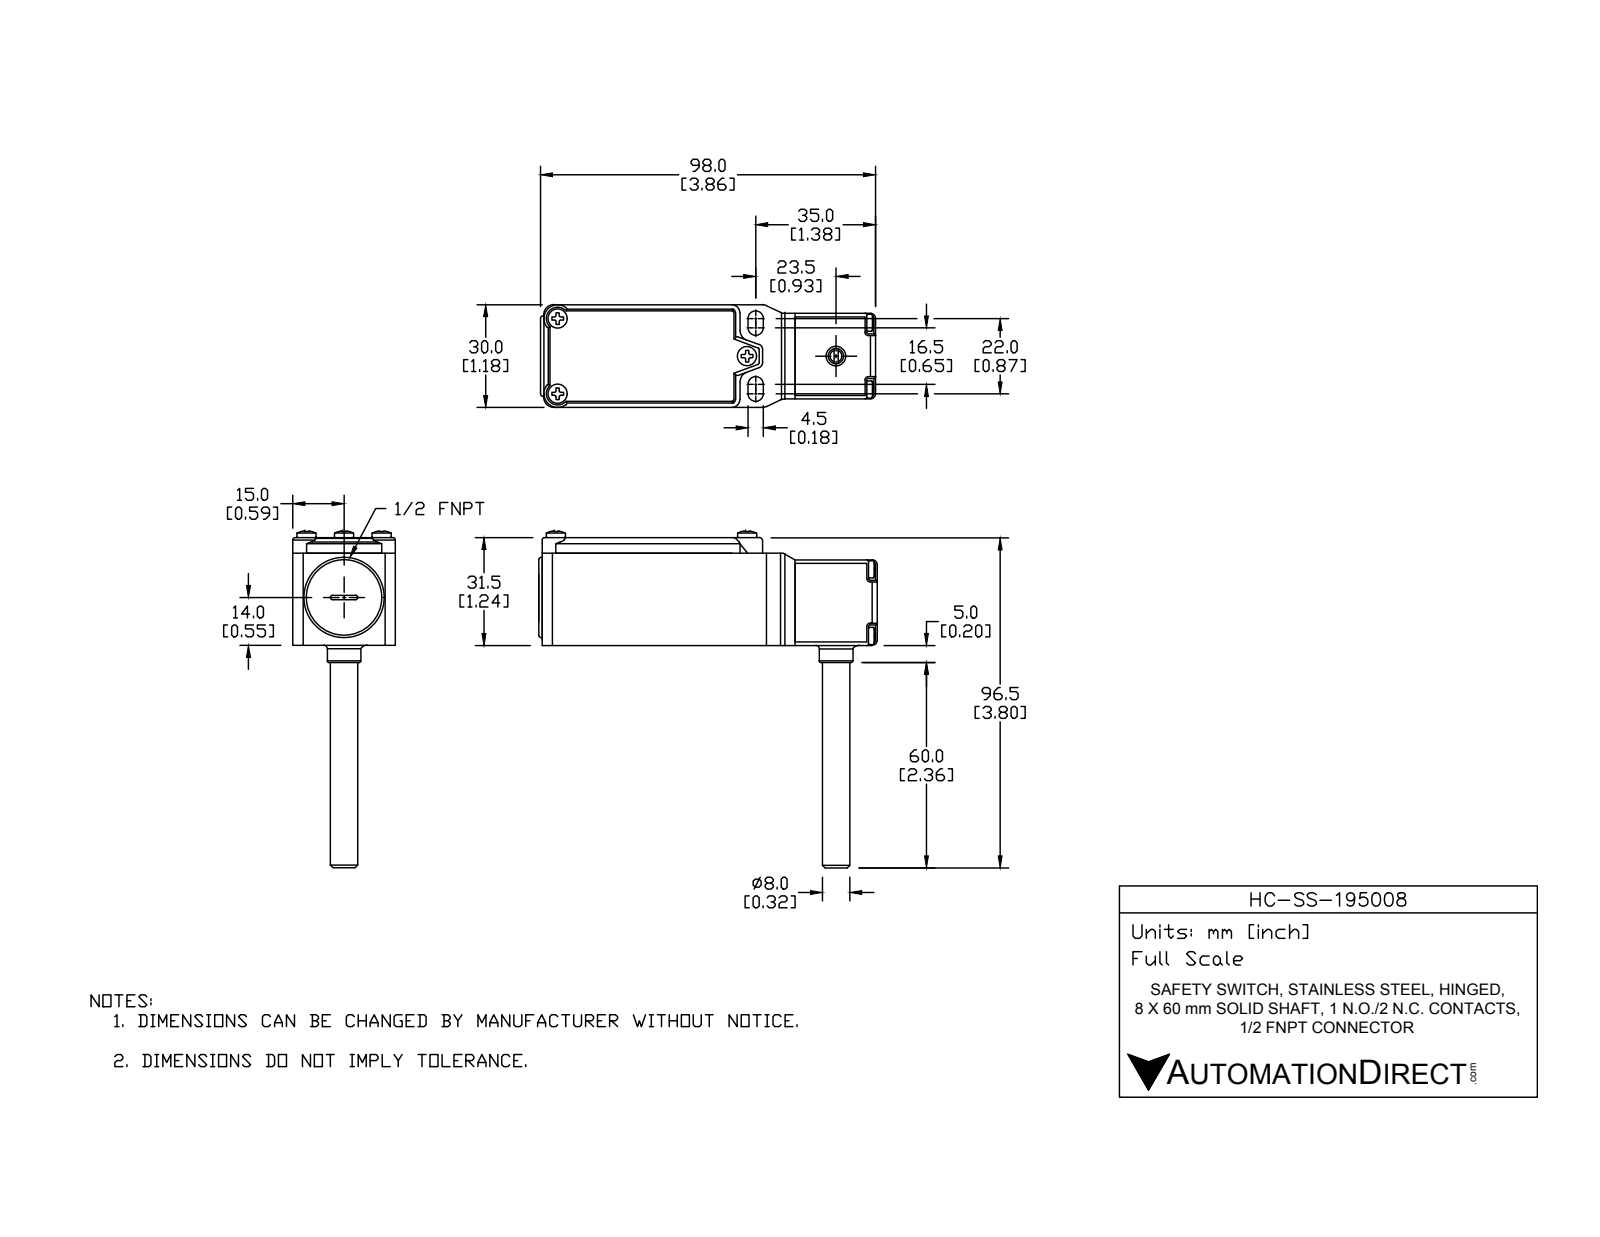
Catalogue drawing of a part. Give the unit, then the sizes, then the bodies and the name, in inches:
Units: inches
Overall size (bounding box): 3.898 × 3.876 × 1.181
Round holes (diameter × count): ⌀0.098 ×8, ⌀0.126 ×7, ⌀0.157 ×3, ⌀0.059 ×2, ⌀0.071 ×2, ⌀0.087 ×2, ⌀0.142 ×2, ⌀0.081 ×1, ⌀0.114 ×1, ⌀0.173 ×1, ⌀0.185 ×1, ⌀0.217 ×1
Round bosses / shafts (diameter × count): ⌀0.118 ×7, ⌀0.197 ×5, ⌀0.138 ×4, ⌀0.22 ×3, ⌀0.925 ×1, ⌀0.697 ×1, ⌀0.386 ×1, ⌀0.315 ×1
Partial cylindrical surfaces — rounded edges, fillets, slot ends (radius × count): R0.02 ×175, R0.039 ×20, R0.012 ×18, R0.006 ×14, R0.028 ×8, R0.118 ×8, R0.059 ×6, R0.089 ×4
Main face-to-face distances: 0.098, 1.142, 0.079, 0.114, 1.067, 1.181, 0.177, 1.24, 0.016, 1.083
Hole centre spacings: 0.543, 0.768, 0.187, 0.245, 0.414, 0.423, 0.426, 0.476
Volume: 2.593 in³ · Surface area: 52.81 in²
Bodies: 13 solids, 1168 faces (347 planar, 466 cylindrical, 355 other)
Part name (STEP PRODUCT): HC-SS-195008
STEP written by: SolidWorks 2014 (AUTOMOTIVE_DESIGN)
